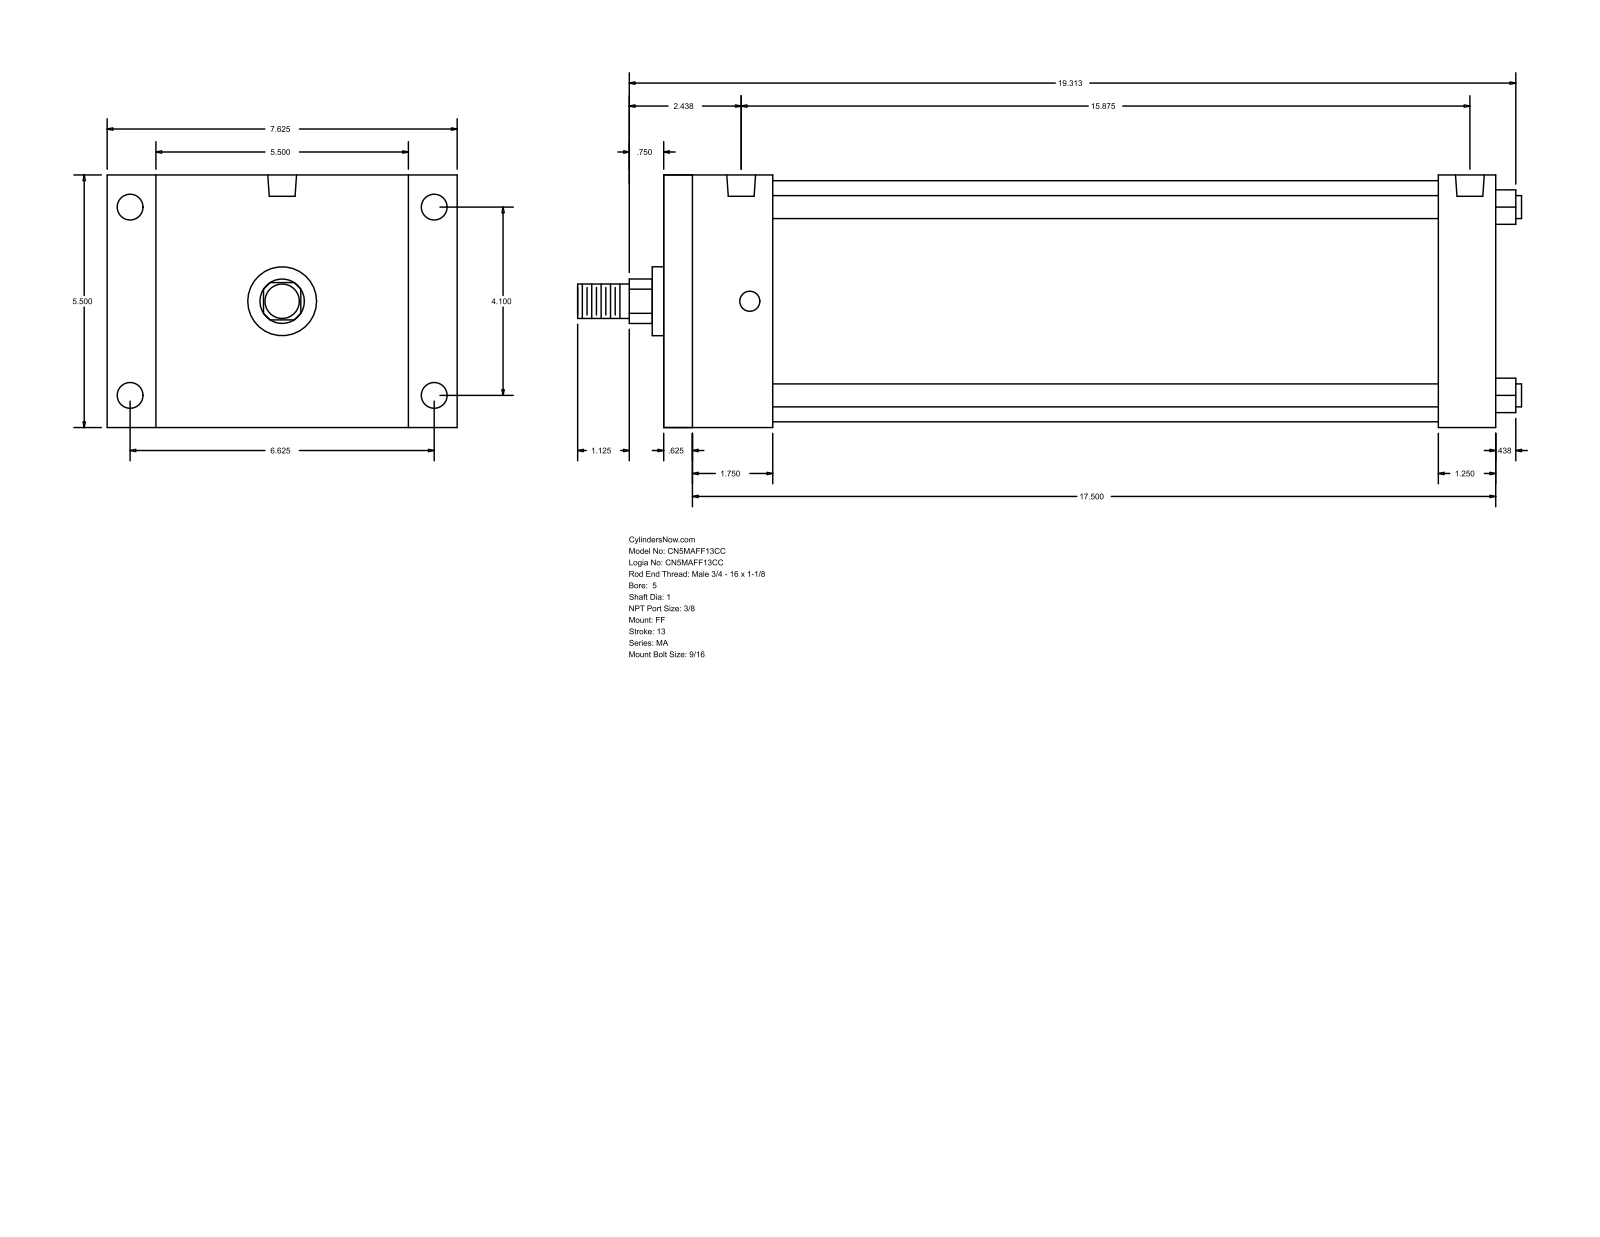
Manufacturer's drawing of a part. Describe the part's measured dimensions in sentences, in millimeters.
The part is named "MA_FF__0500_1". Its 3-D file was written by "GSSL Pune (CONFIG_CONTROL_DESIGN)". It is 0 solids with 92 faces: 64 planar, 28 cylindrical and 0 other. Overall it measures 522.29 by 193.68 by 139.7 millimeters. Round holes: 4 of diameter 11.11, 4 of diameter 14.29, 2 of diameter 15.93. Round bosses or shafts: 4 of diameter 12.7, 1 of diameter 133.35, 1 of diameter 38.1, 1 of diameter 25.4, 1 of diameter 19.05. Partial cylindrical surfaces (rounded edges, fillets, slot ends): 1 of radius 12.29. The main face-to-face distances are 139.7, 460.38, 15.87, 444.51, 428.63, 412.76, 31.75, 60.33, 44.46, 368.3. The hole center spacings are 4.76, 104.14, 168.28, 197.9, 393.71, 398.47, 403.23.
